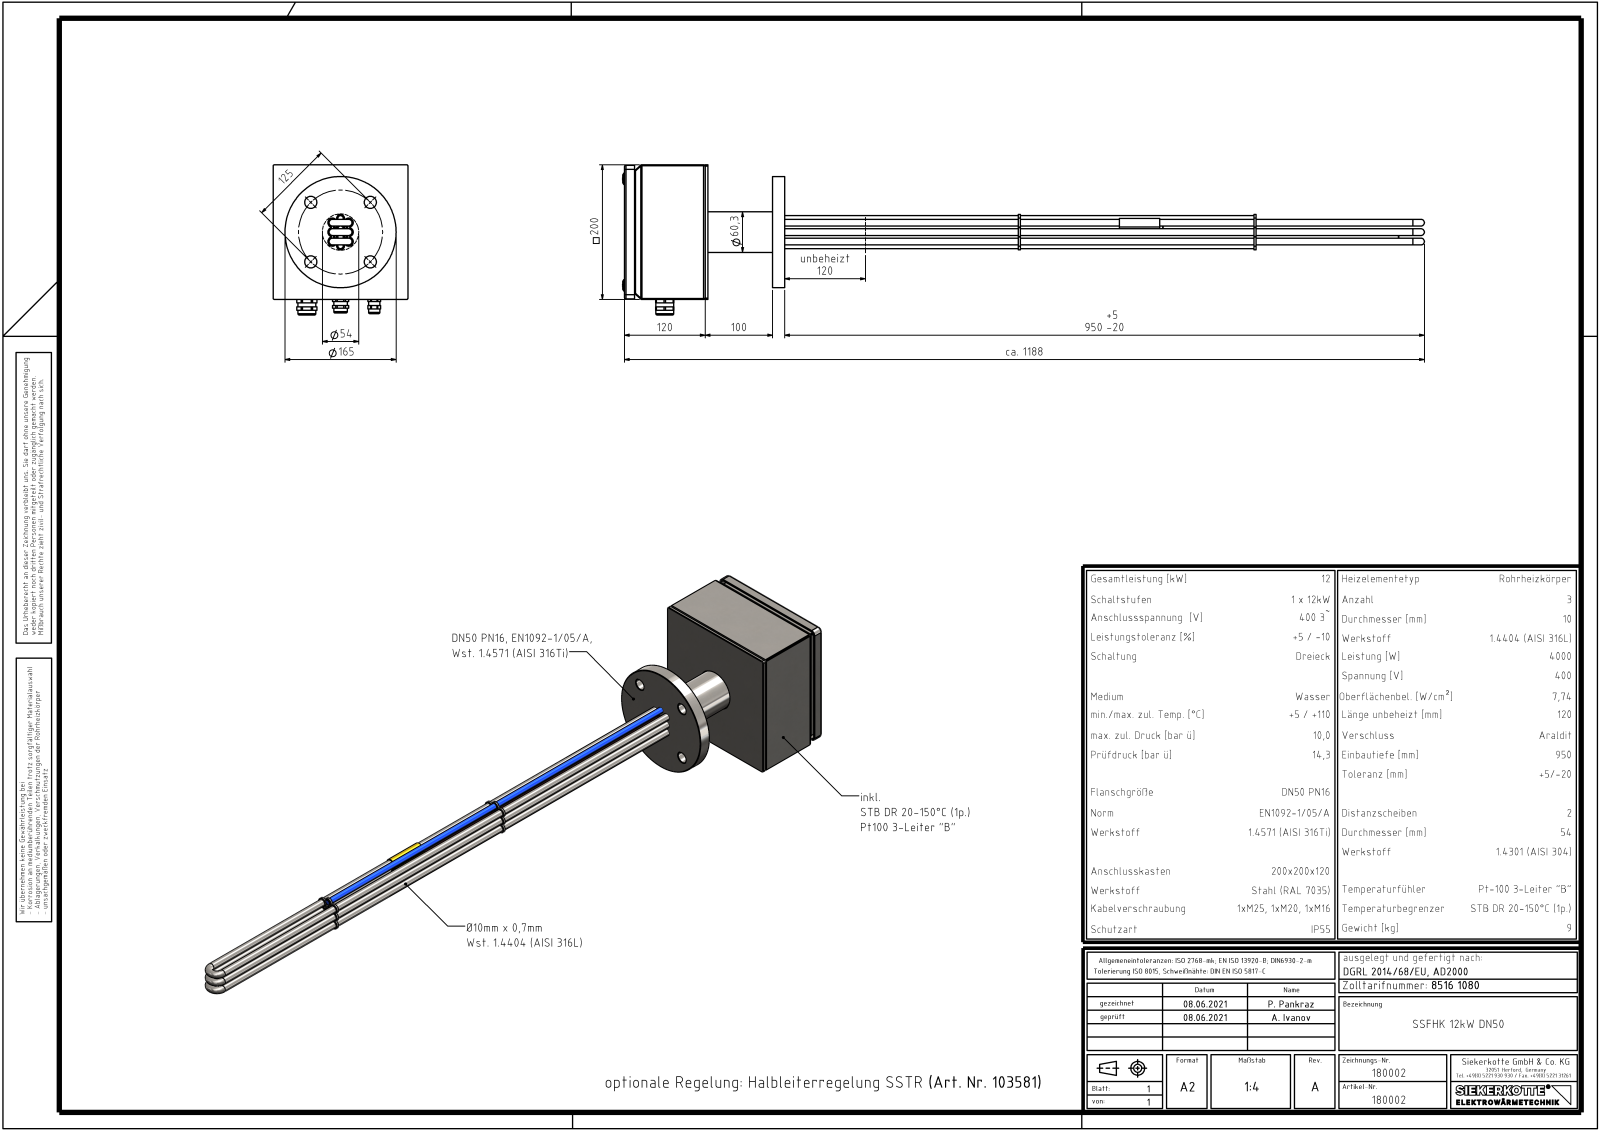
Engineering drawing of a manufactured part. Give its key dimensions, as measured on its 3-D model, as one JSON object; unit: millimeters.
{"part_name": "KV M20 WT MS^Kabelverschraubung_SSFHK; Kabelverschraubung^SSFHK_M25+M20+M16; AK 200x200x120^Anschlusskasten_SSFHK; Kühlstrecke^SSFHK_DN50 (+8 more)", "step_written_by": "SolidWorks 2021 (AUTOMOTIVE_DESIGN)", "units": "millimeters", "bodies": {"solids": 24, "faces": 1243, "planar": 344, "cylindrical": 619, "other": 280}, "overall_size": [1190.75, 223, 200], "volume_mm3": 1089000, "surface_area_mm2": 981029, "round_holes": [[10.2, 10], [8, 6], [10.7, 6], [5, 4], [8.4, 4], [8.7, 4], [18, 4], [8.5, 3], [7, 2], [9.2, 2], [9.7, 2], [6.2, 1]], "round_bosses_or_shafts": [[10, 10], [8, 6], [9.4, 4], [5.3, 4], [5, 4], [4.3, 4], [2.7, 4], [11.5, 2]], "partial_cylinders_radius": [[0.5, 54], [1.25, 24], [2.5, 24], [5, 8], [2, 6], [2.25, 6], [6.85, 6], [6, 5]], "face_to_face_distances": [1.25, 198.75, 118.75, 200, 4, 120, 124, 197.5, 122.75, 118], "hole_center_spacings": [128.01, 129.25, 159, 1.41, 13.89, 14, 18.44, 27.78]}
